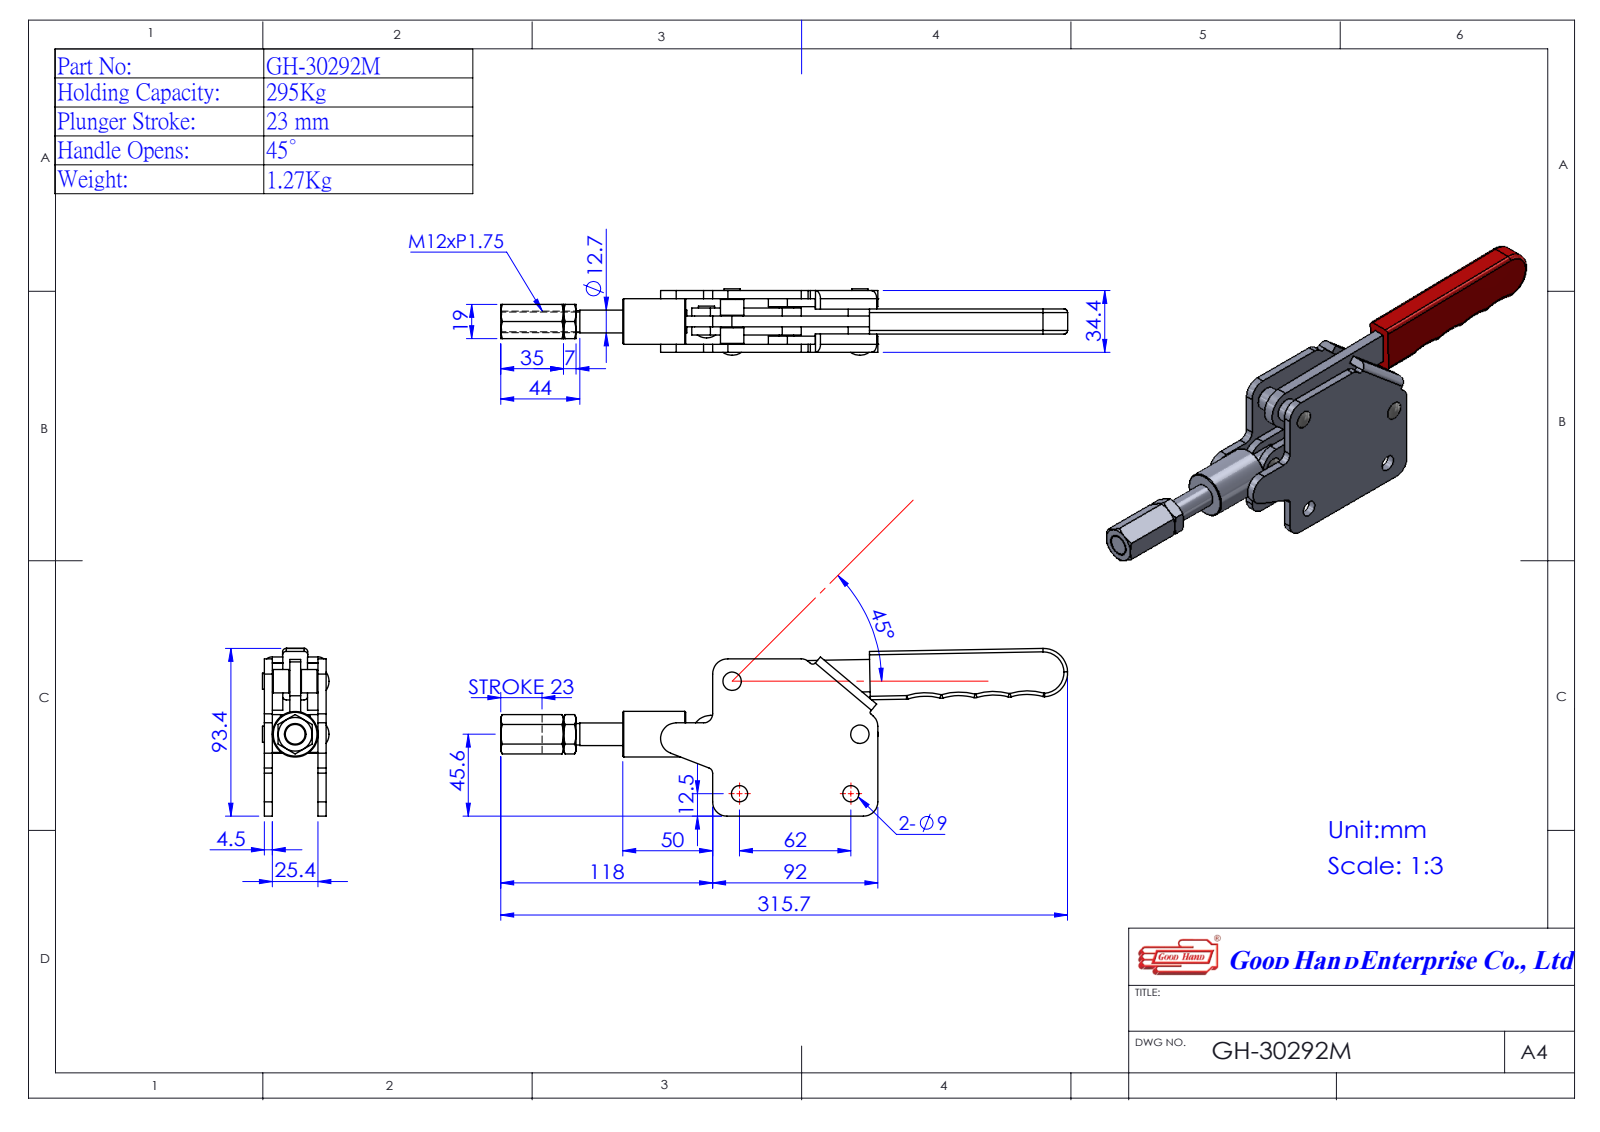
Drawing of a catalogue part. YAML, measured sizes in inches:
part_name: "GH-36092_BASE; GH-30292M(簡化); Group1^GH-30292M(簡化); Group2^GH-30292M(簡化) (+4 more)"
step_written_by: "SolidWorks 2016 (AUTOMOTIVE_DESIGN)"
units: inches
bodies: {solids: 9, faces: 223, planar: 95, cylindrical: 110, other: 18}
overall_size: [12.431, 3.529, 1.457]
volume: 11.53
surface_area: 126.7
round_holes:
  - {diameter: 0.236, count: 4}
  - {diameter: 0.354, count: 2}
  - {diameter: 0.472, count: 1}
  - {diameter: 0.5, count: 1}
round_bosses_or_shafts:
  - {diameter: 0.354, count: 3}
  - {diameter: 1, count: 1}
  - {diameter: 0.512, count: 1}
  - {diameter: 0.223, count: 1}
partial_cylinders:
  - {radius: 0.118, count: 8}
  - {radius: 0.039, count: 4}
  - {radius: 0.413, count: 4}
  - {radius: 1.26, count: 4}
  - {radius: 0.315, count: 2}
  - {radius: 0.079, count: 1}
  - {radius: 0.177, count: 1}
  - {radius: 0.197, count: 1}
face_to_face_distances: [0.177, 1.177, 1, 0.382, 0.795, 0.618, 1.354, 0.559, 0.394, 0.402]
hole_center_spacings: [1.29, 1.318, 1.49, 1.61, 1.631, 1.689, 1.752, 1.897]
